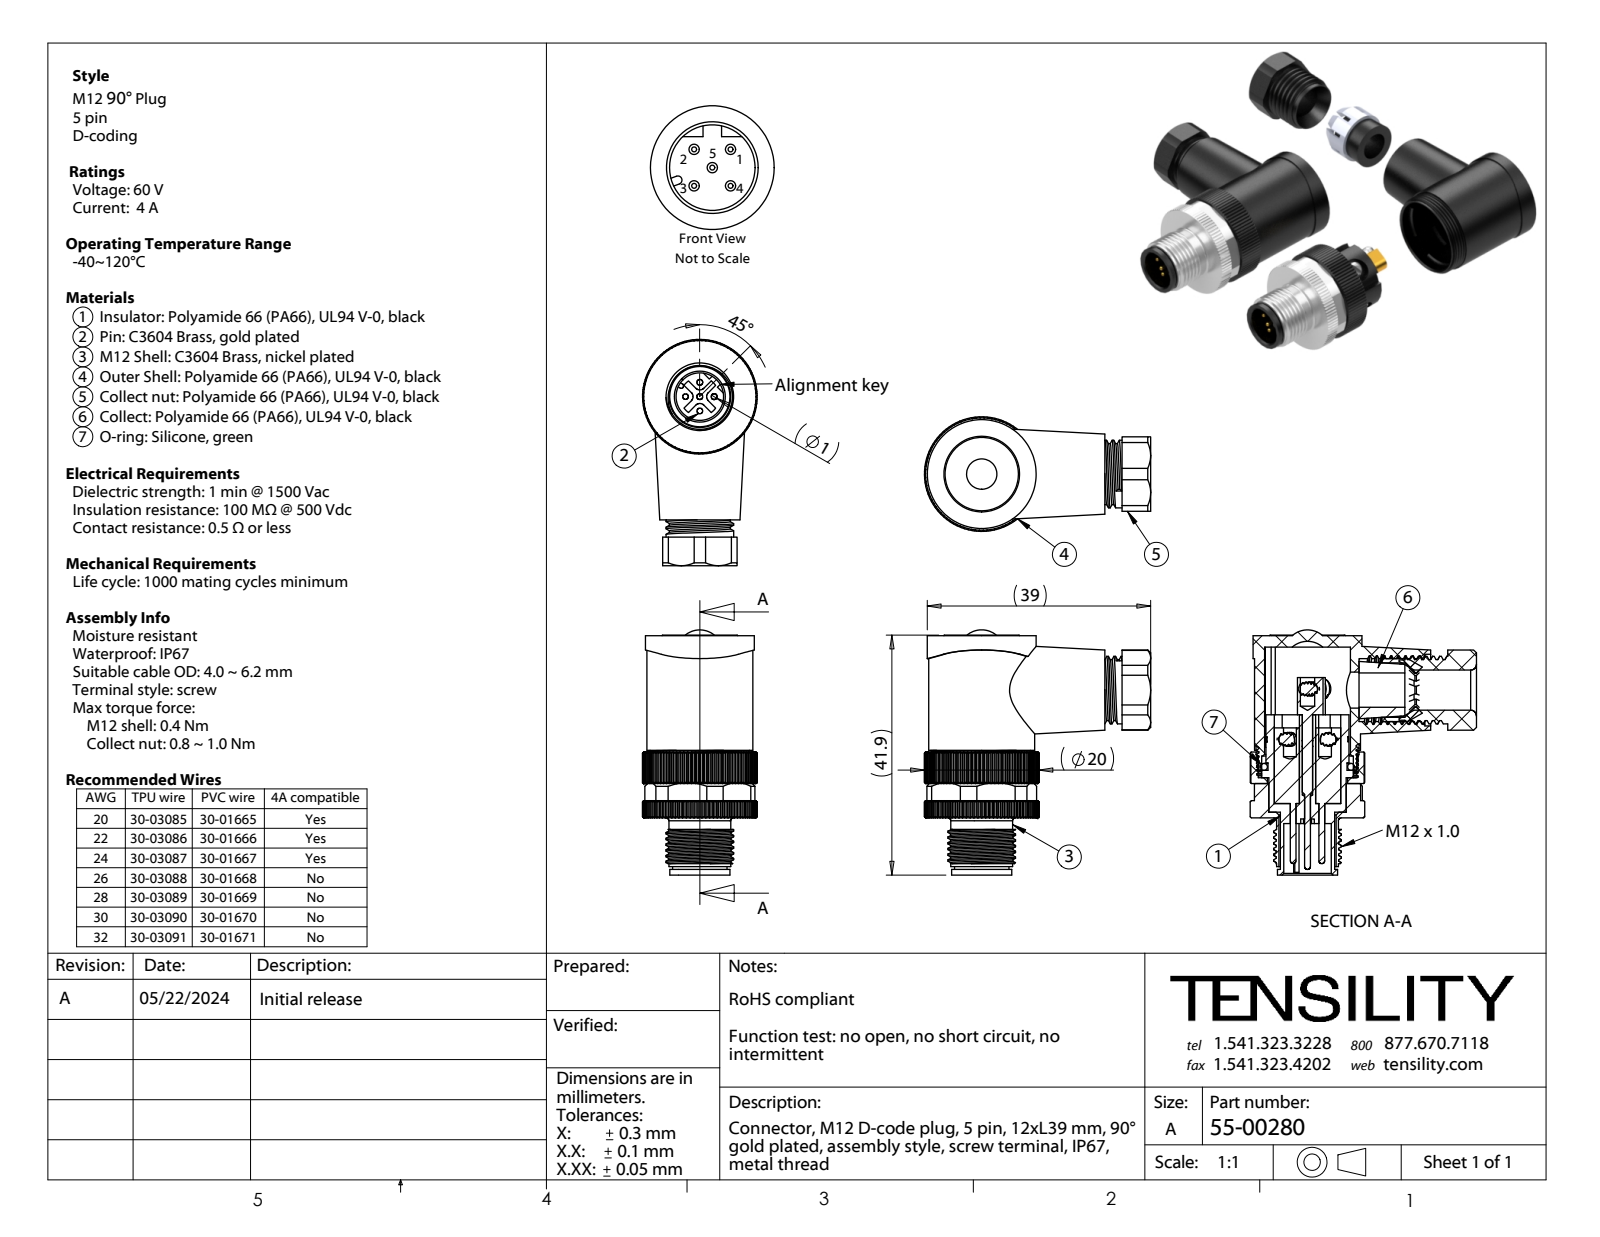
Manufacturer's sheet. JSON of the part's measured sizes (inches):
{"part_name": "55-00280-05; 55-00280-01; 55-00280-02; 55-00280-04 (+8 more)", "step_written_by": "SolidWorks 2021 (CONFIG_CONTROL_DESIGN)", "units": "inches", "bodies": {"solids": 18, "faces": 1654, "planar": 579, "cylindrical": 539, "other": 536}, "overall_size": [1.685, 1.555, 0.787], "volume_in3": 0.558, "surface_area_in2": 22.1, "round_holes": [[0.098, 9], [0.039, 5], [0.081, 5], [0.197, 4], [0.236, 1], [0.248, 1], [0.276, 1], [0.327, 1], [0.374, 1], [0.394, 1], [0.433, 1], [0.492, 1]], "round_bosses_or_shafts": [[0.138, 5], [0.094, 5], [0.465, 2], [0.413, 2], [0.787, 1], [0.748, 1], [0.728, 1], [0.701, 1]], "partial_cylinders_radius": [[0.069, 5], [0.039, 4], [0.016, 1], [0.134, 1], [0.254, 1], [0.256, 1], [0.276, 1], [0.38, 1]], "face_to_face_distances": [0.039, 0.236, 1.016, 0.079, 0.177, 0.276, 0.546, 1.252, 0.709, 0.138], "hole_center_spacings": [0.202, 0.202, 0.031, 0.098, 0.123, 0.139, 0.143, 0.171]}
